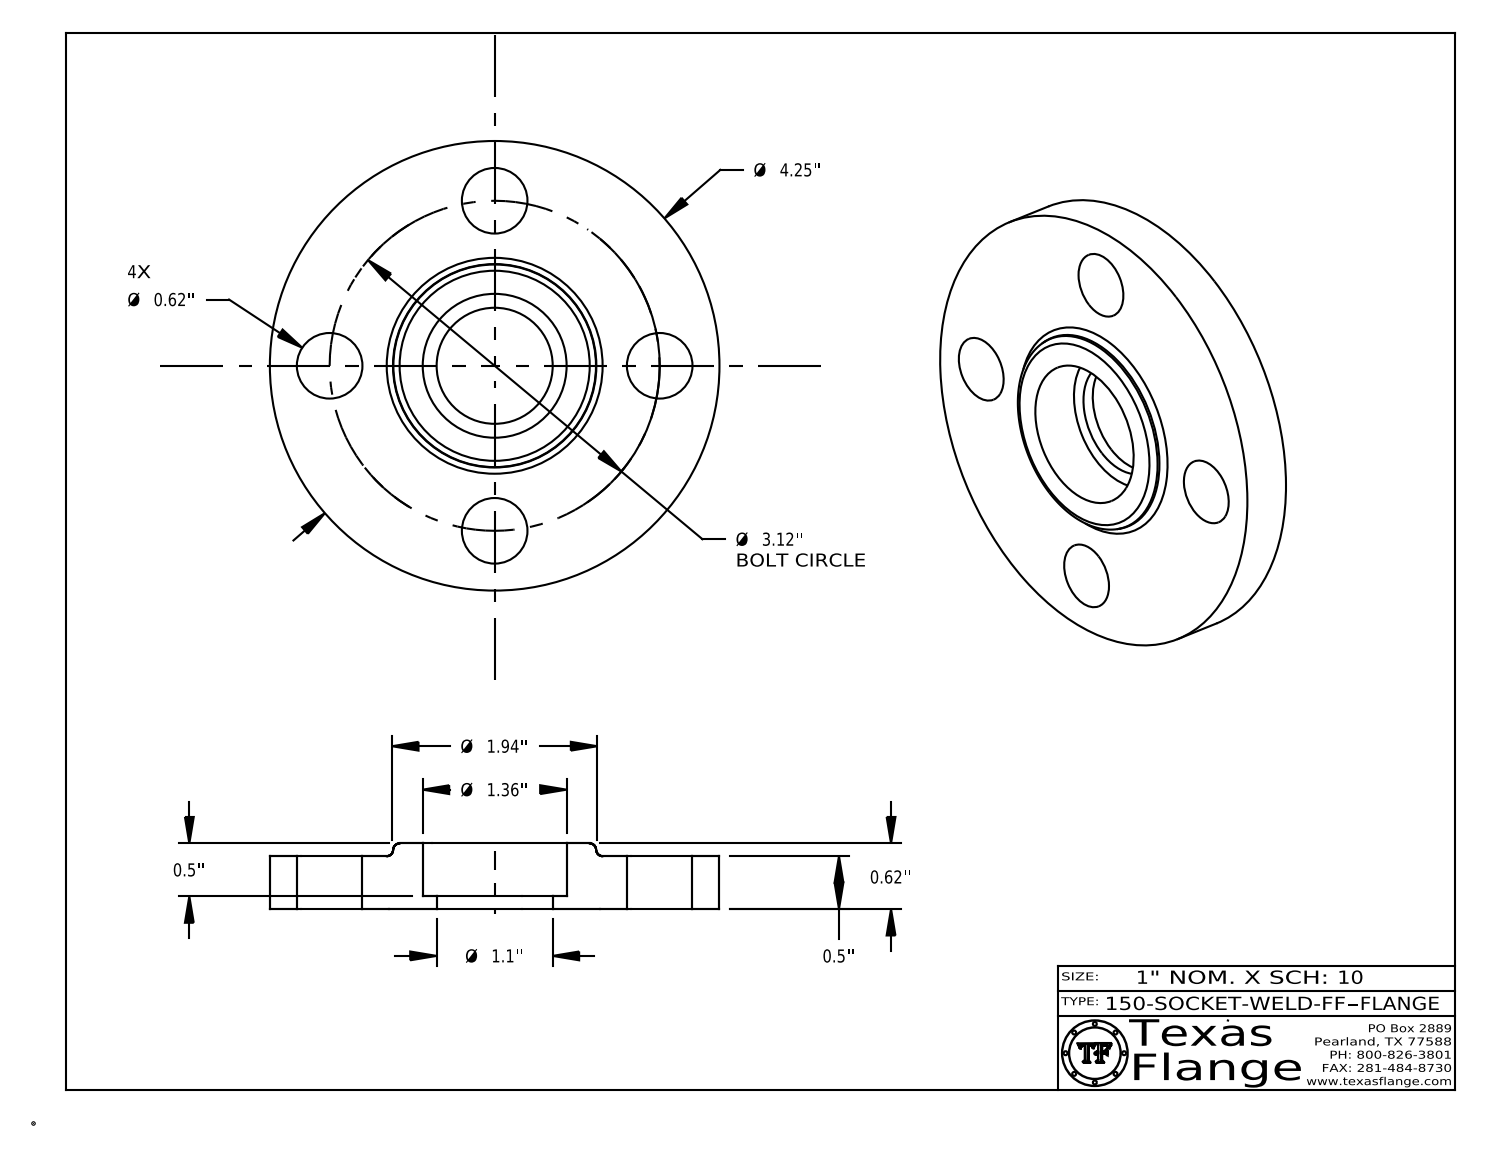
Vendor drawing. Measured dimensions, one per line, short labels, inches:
name: 150-SOCKET-WELD-FF
written by: CATIA V5 STEP AP214 (AUTOMOTIVE_DESIGN)
unit: in
bodies: 1 solid, 410 faces (370 planar, 34 cylindrical, 6 other)
size: 4.25 × 4.25 × 0.62
volume: 5.996 in³; area: 37.68 in²
holes: 4× ⌀0.62, 1× ⌀0.495, 1× ⌀1.097, 1× ⌀1.36
bosses: 8× ⌀0.03, 1× ⌀4.25, 1× ⌀0.39
face distances: 0.5, 0.12, 0.62, 0.38, 0.485, 0.365, 0.015, 0.135, 0.148, 0.144
hole spacings: 1.56, 2.206, 1.194, 2.882, 3.12, 1.56
